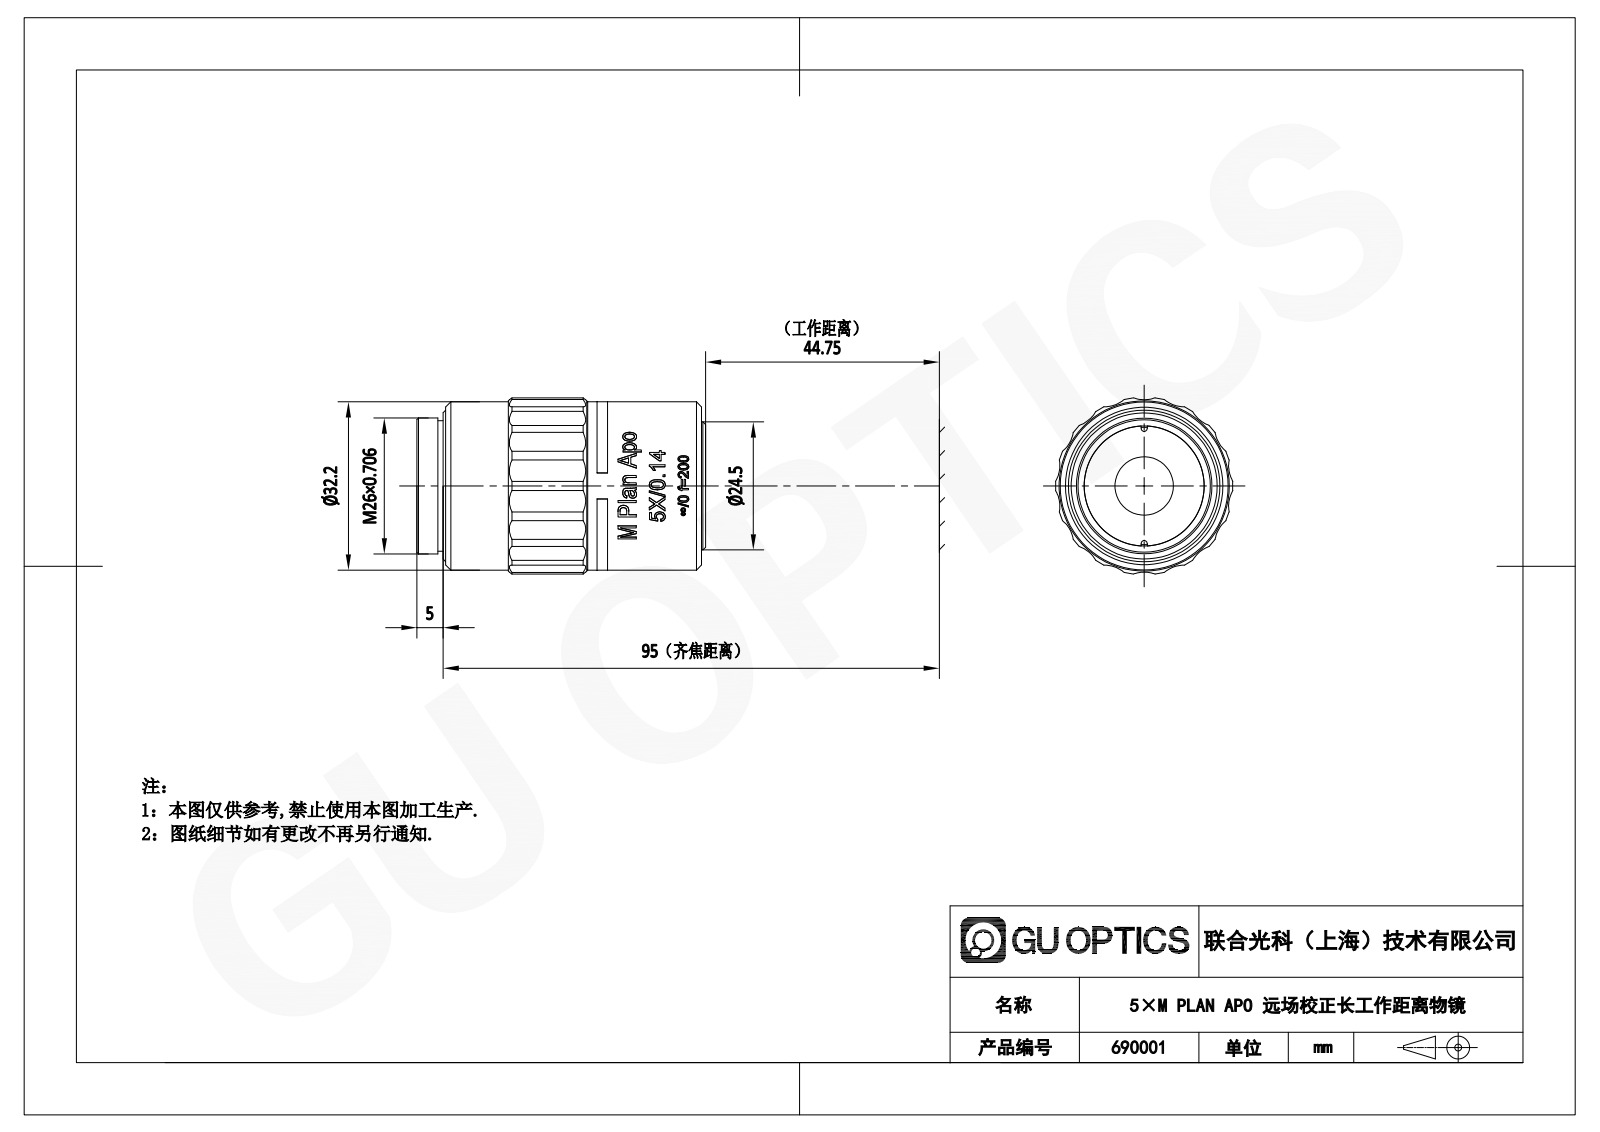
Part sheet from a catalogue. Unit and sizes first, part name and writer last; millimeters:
Units: millimetres
Overall size (bounding box): 55.25 × 33.66 × 33.66
Round holes (diameter × count): ⌀18.95 ×1, ⌀20.16 ×1
Round bosses / shafts (diameter × count): ⌀32.2 ×1, ⌀26 ×1, ⌀25 ×1, ⌀24.5 ×1
Partial cylindrical surfaces — rounded edges, fillets, slot ends (radius × count): R1.71 ×20, R16.87 ×1
Main face-to-face distances: 0.75, 54.5, 53.75, 5, 4.25, 49.5, 55.25, 50.25, 32.5, 31.75
Volume: 43 577 mm³ · Surface area: 7 341 mm²
Bodies: 1 solid, 62 faces (10 planar, 47 cylindrical, 5 other)
Part name (STEP PRODUCT): 690001
STEP written by: SolidWorks 2020 (CONFIG_CONTROL_DESIGN)
